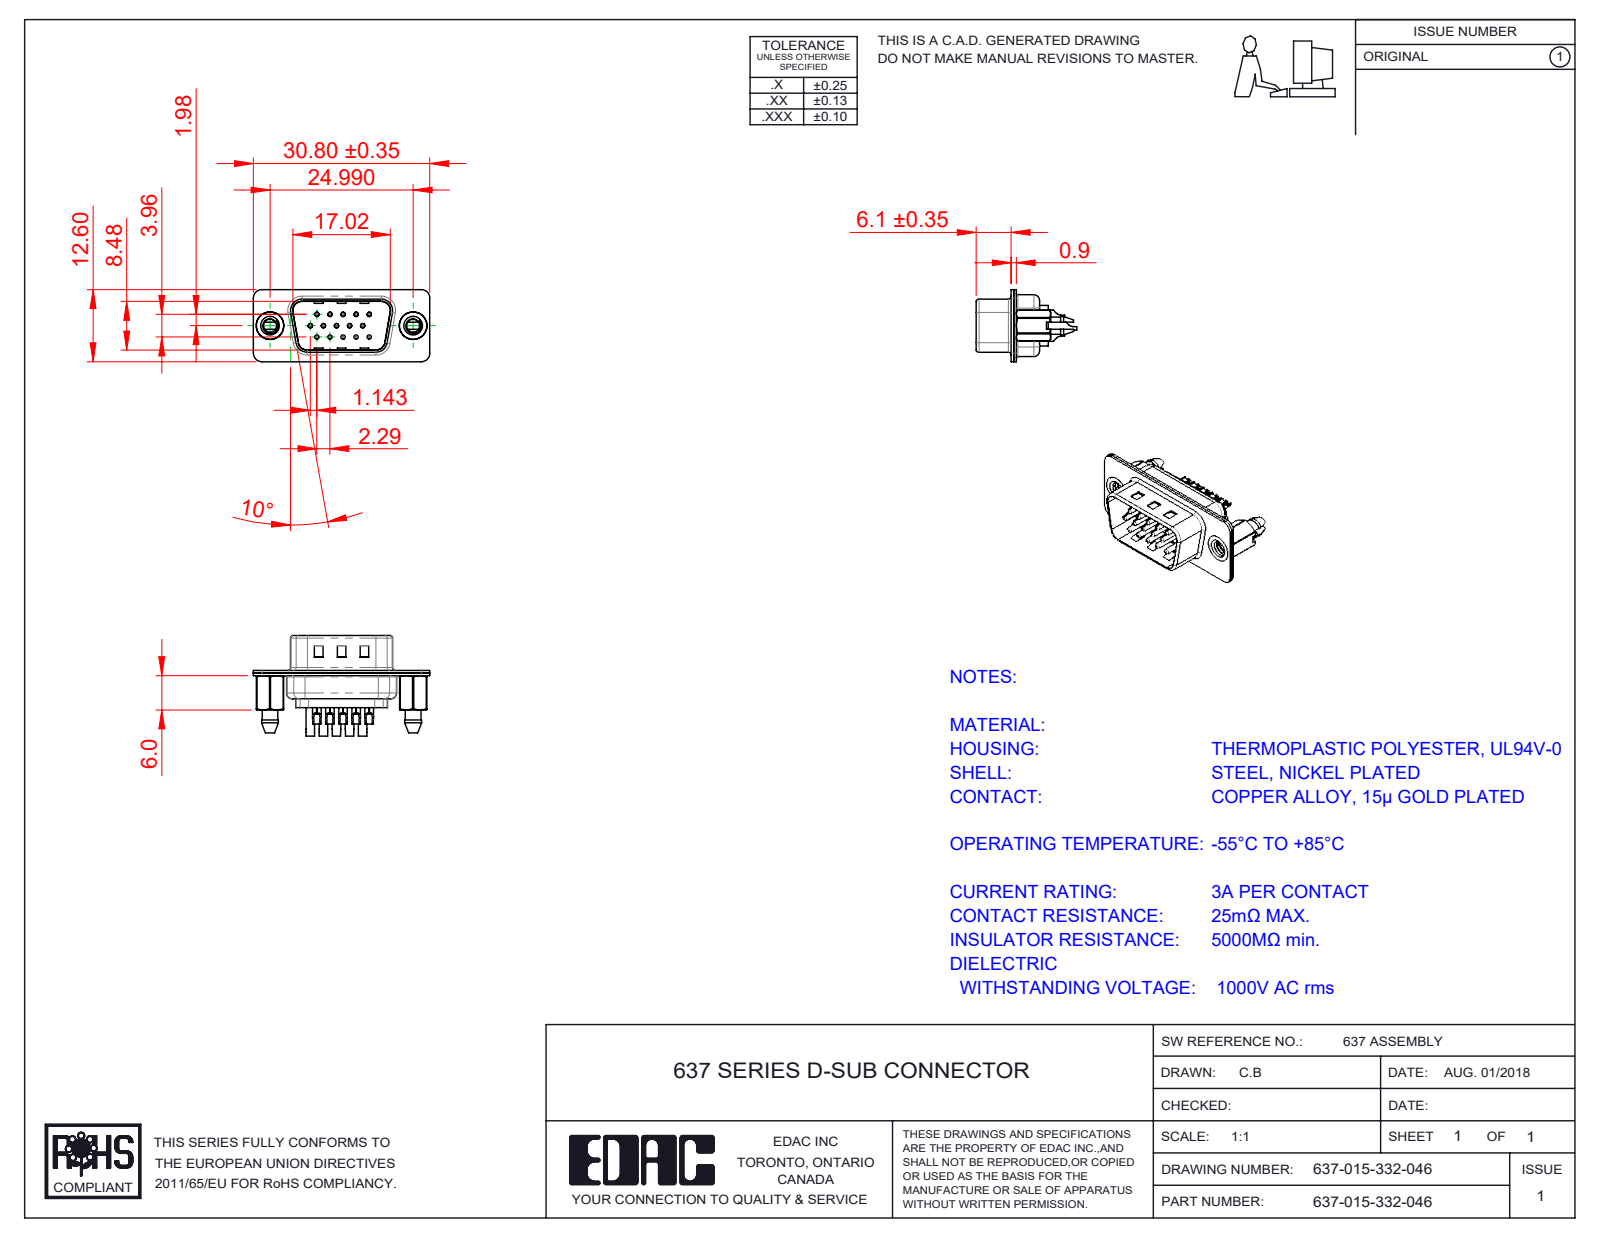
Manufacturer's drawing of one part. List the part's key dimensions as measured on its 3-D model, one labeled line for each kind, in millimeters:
Part name (STEP PRODUCT): 637 Shell Front_15 Contacts; 637 Contact Row 1_32; 637 Housing_15 Contacts; 637 Contact Row 2_32 (+4 more)
STEP written by: SolidWorks 2020 (CONFIG_CONTROL_DESIGN)
Units: millimetres
Bodies: 20 solids, 1338 faces (349 planar, 596 cylindrical, 393 other)
Overall size (bounding box): 30.8 × 17.55 × 12.6
Volume: 1 444 mm³ · Surface area: 5 064 mm²
Round holes (diameter × count): ⌀0.35 ×15, ⌀1.1 ×15, ⌀1.6 ×15, ⌀2.26 ×2, ⌀4 ×2, ⌀4.8 ×2
Round bosses / shafts (diameter × count): ⌀2 ×15, ⌀1.5 ×15, ⌀0.75 ×15, ⌀4.9 ×2
Partial cylindrical surfaces — rounded edges, fillets, slot ends (radius × count): R1.5 ×18, R2 ×12, R0.5 ×8, R1 ×7, R1.6 ×6, R0.25 ×4, R0.55 ×4, R0.7 ×4
Main face-to-face distances: 0.45, 0.4, 0.9, 0.7, 8.88, 8.48, 6.5, 1.05, 4.55, 0.31
Hole centre spacings: 3.96, 2.28, 4.57, 2.29, 6.05, 6.86, 7.92, 6.04
